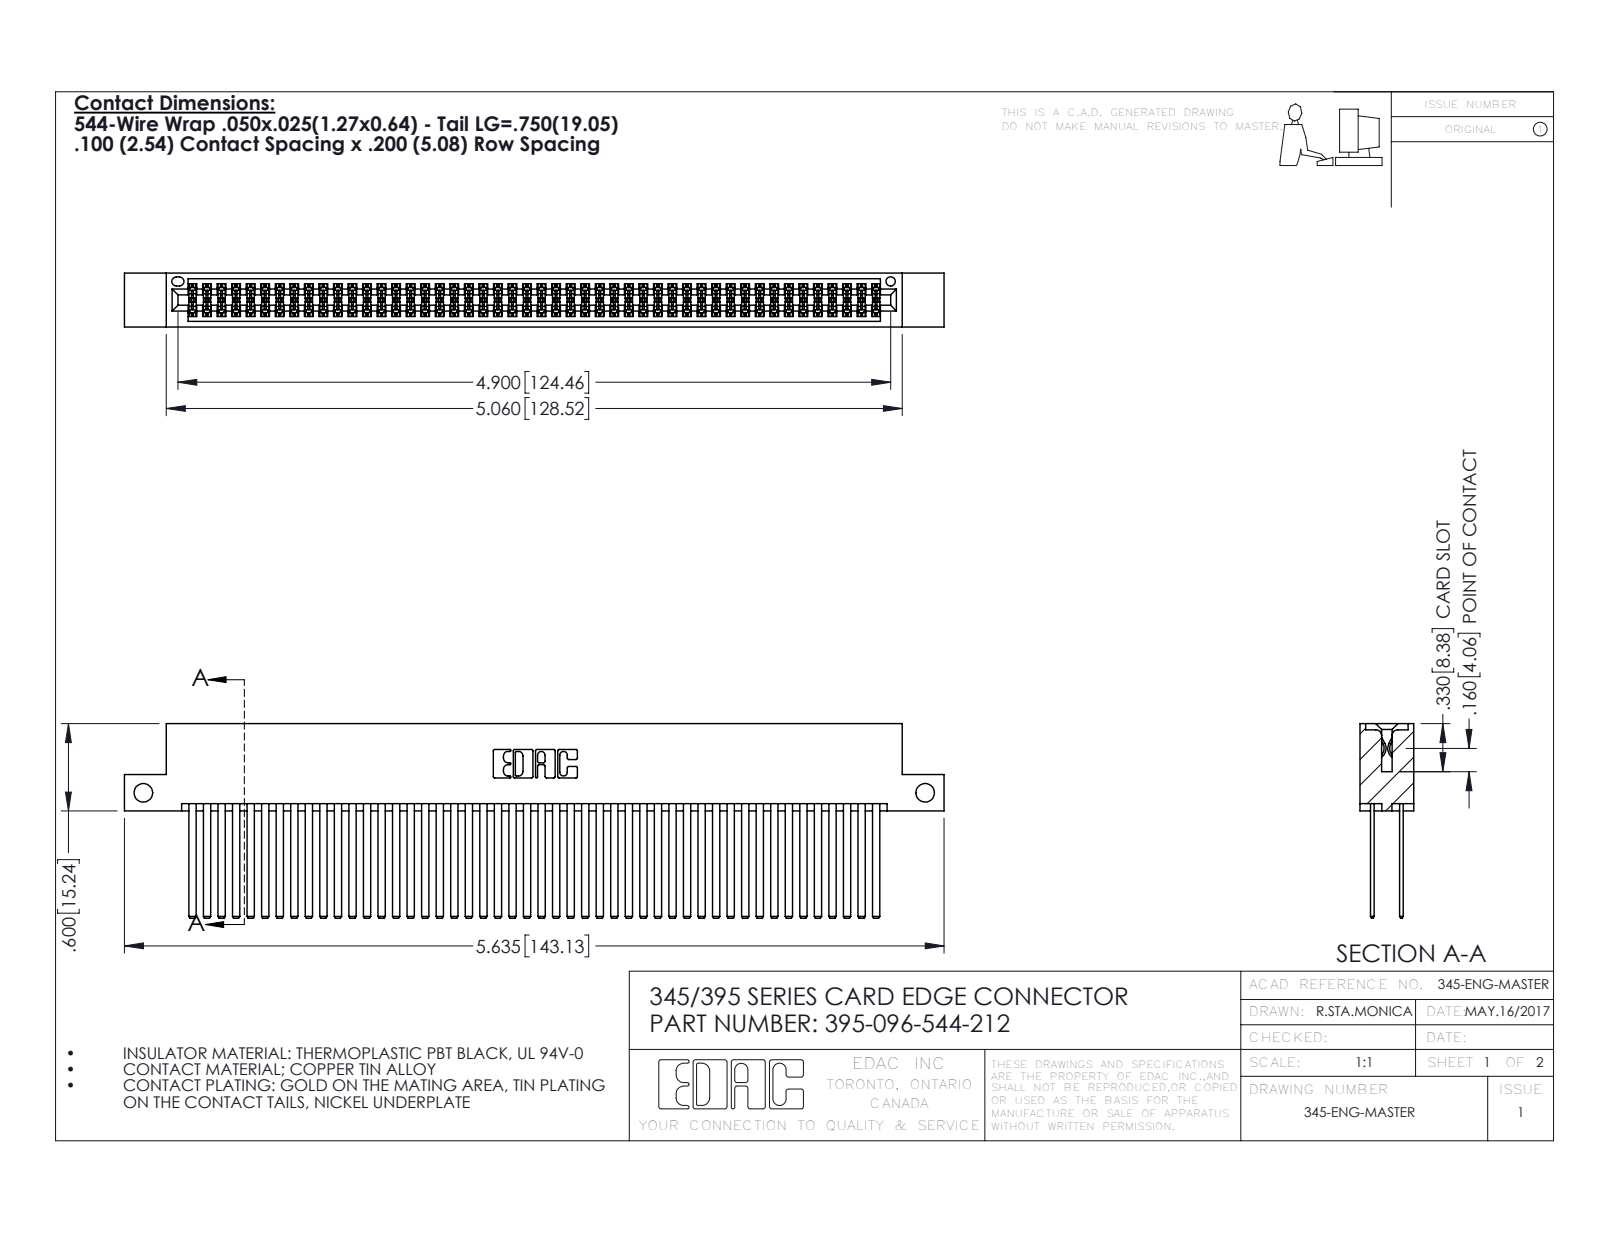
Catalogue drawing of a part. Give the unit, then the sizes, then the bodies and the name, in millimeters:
Units: millimetres
Overall size (bounding box): 143.1 × 34 × 9.4
Round holes (diameter × count): ⌀3.3 ×2, ⌀1.6 ×1
Partial cylindrical surfaces — rounded edges, fillets, slot ends (radius × count): R0.2 ×144, R0.3 ×22, R0.2 ×6, R0.8 ×6, R0.7 ×3, R0.4 ×2, R0.5 ×2, R0.6 ×2
Main face-to-face distances: 5.1, 0.6, 7.6, 1.8, 2.5, 6.9, 5.7, 4.4, 9.4, 1.3
Hole centre spacings: 136.5
Volume: 15 200 mm³ · Surface area: 26 420 mm²
Bodies: 97 solids, 4350 faces (2864 planar, 1486 cylindrical, 0 other)
Part name (STEP PRODUCT): 345 Part_Flush Mounting Lugs - Side Mount; 345-292-001_345-293-144; 395-096-544-212
STEP written by: SolidWorks 2016 (CONFIG_CONTROL_DESIGN)
